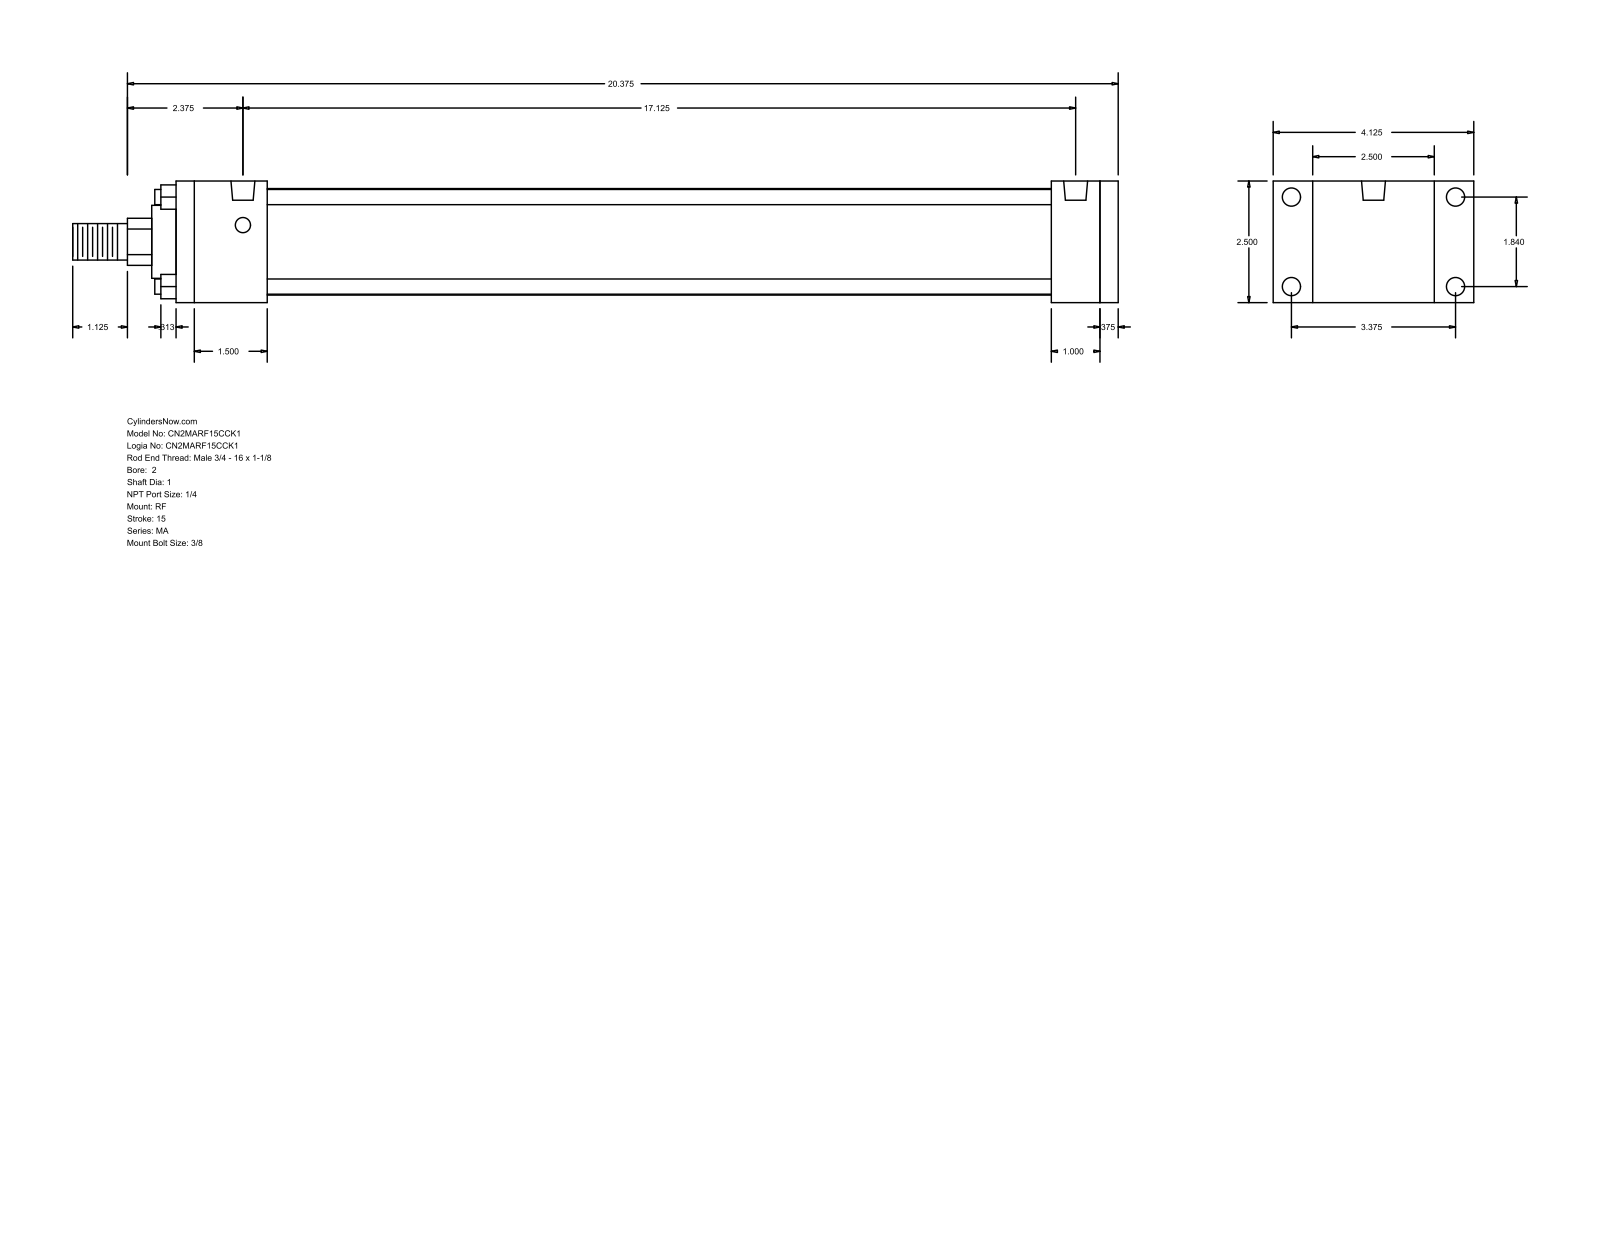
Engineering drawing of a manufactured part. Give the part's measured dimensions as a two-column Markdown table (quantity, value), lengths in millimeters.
| quantity | value |
| --- | --- |
| part name | MA_RF__0200_1 |
| STEP written by | GSSL Pune (CONFIG_CONTROL_DESIGN) |
| units | millimeters |
| bodies | 0 solids, 92 faces (64 planar, 28 cylindrical, 0 other) |
| overall size | 546.1 × 104.78 × 63.5 |
| round holes (diameter × count) | 7.94 × 4, 9.53 × 4, 12.49 × 2 |
| round bosses / shafts (diameter × count) | 7.94 × 4, 55.63 × 1, 38.1 × 1, 25.4 × 1, 19.05 × 1 |
| partial cylindrical surfaces (radius × count) | 12.29 × 1 |
| main face-to-face distances | 63.5, 482.6, 9.52, 492.12, 25.4, 20.64, 12.7, 47.63, 434.97, 444.49 |
| hole center spacings | 46.74, 85.72, 97.63, 434.97 |
